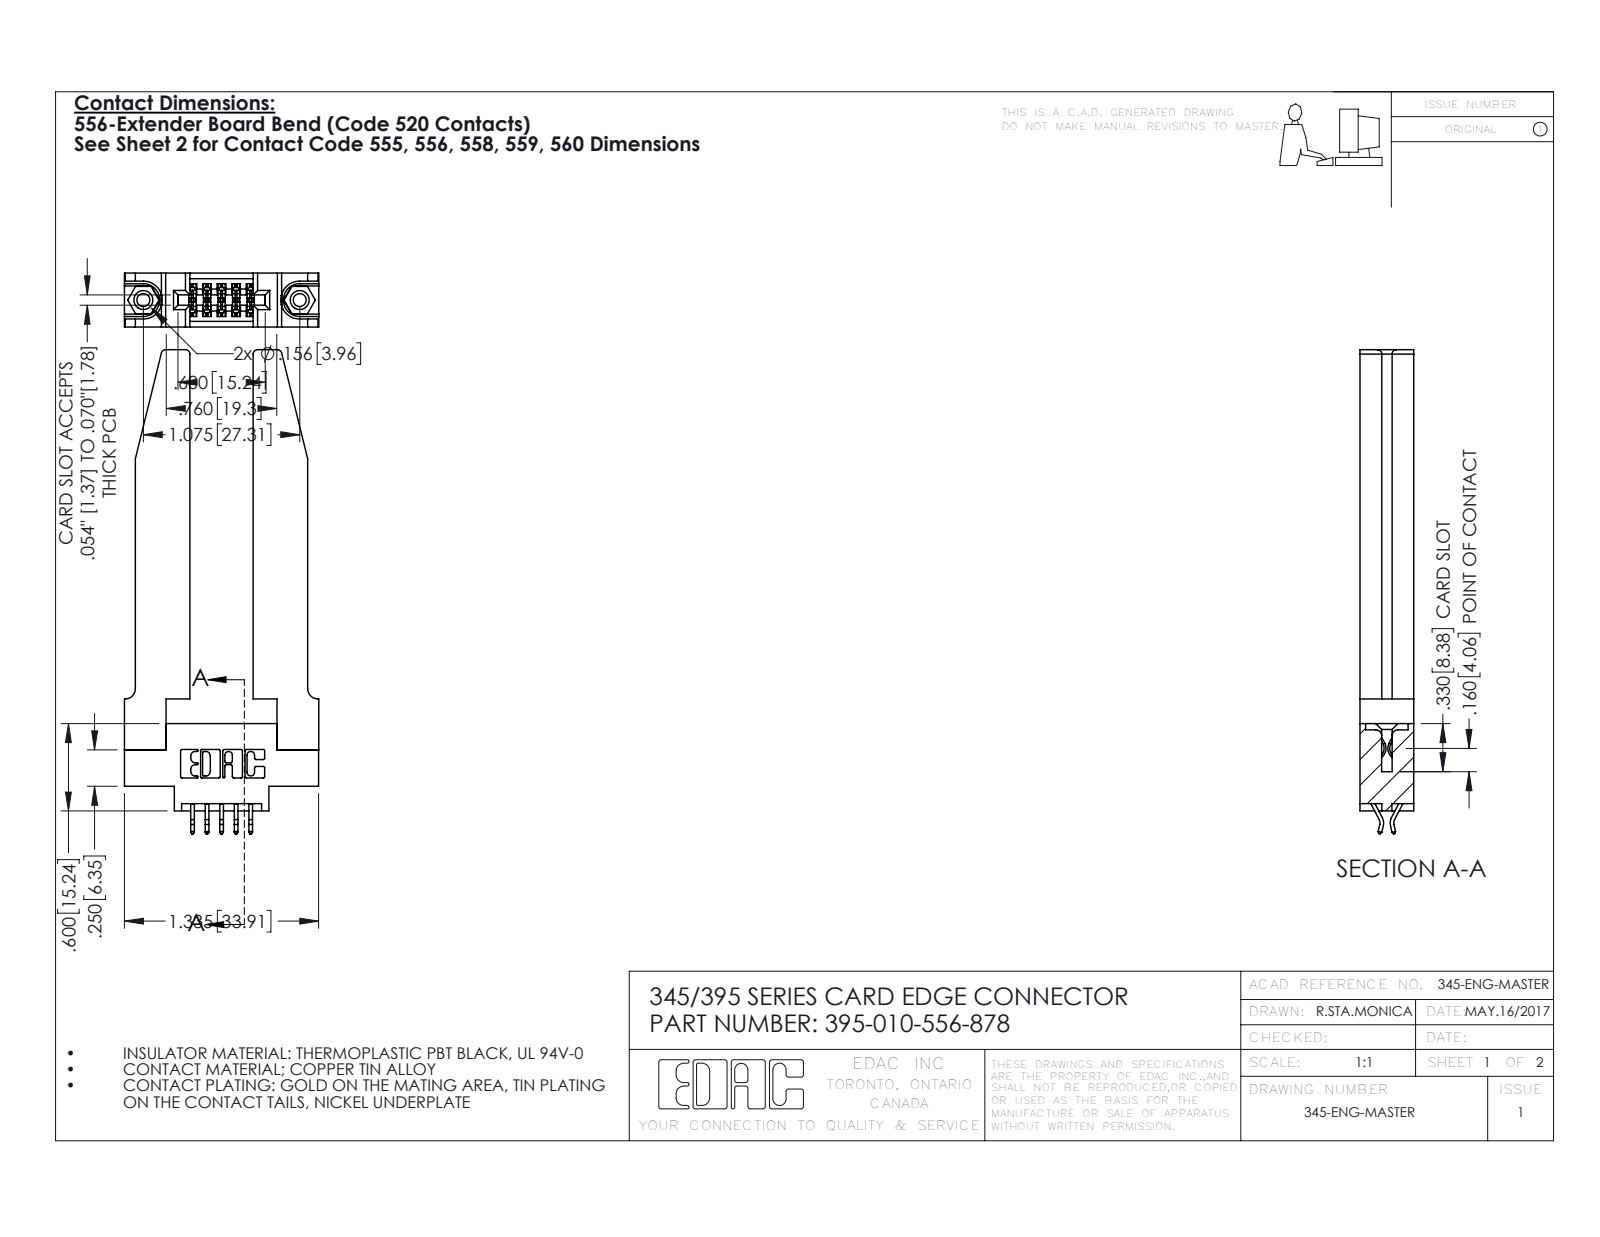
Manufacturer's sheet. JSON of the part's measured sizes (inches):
{"part_name": "345-220-078_345-220-078; 345-292-001_556 Tail; 395-010-556-878; 345-250-001_345-250-001-102 (+1 more)", "step_written_by": "SolidWorks 2016 (CONFIG_CONTROL_DESIGN)", "units": "inches", "bodies": {"solids": 15, "faces": 924, "planar": 596, "cylindrical": 276, "other": 52}, "overall_size": [3.327, 1.336, 0.37], "volume_in3": 0.647, "surface_area_in2": 16.2, "round_holes": [[0.089, 2], [0.125, 2], [0.156, 2], [0.064, 1]], "round_bosses_or_shafts": [[0.155, 2]], "partial_cylinders_radius": [[0.01, 22], [0.006, 15], [0.03, 8], [0.007, 6], [0.031, 6], [0.026, 3], [0.01, 2], [0.014, 2]], "face_to_face_distances": [0.37, 0.15, 0.22, 0.435, 0.148, 0.072, 0.298, 0.077, 0.095, 0.071], "hole_center_spacings": [0.27, 0.847, 1.075]}
